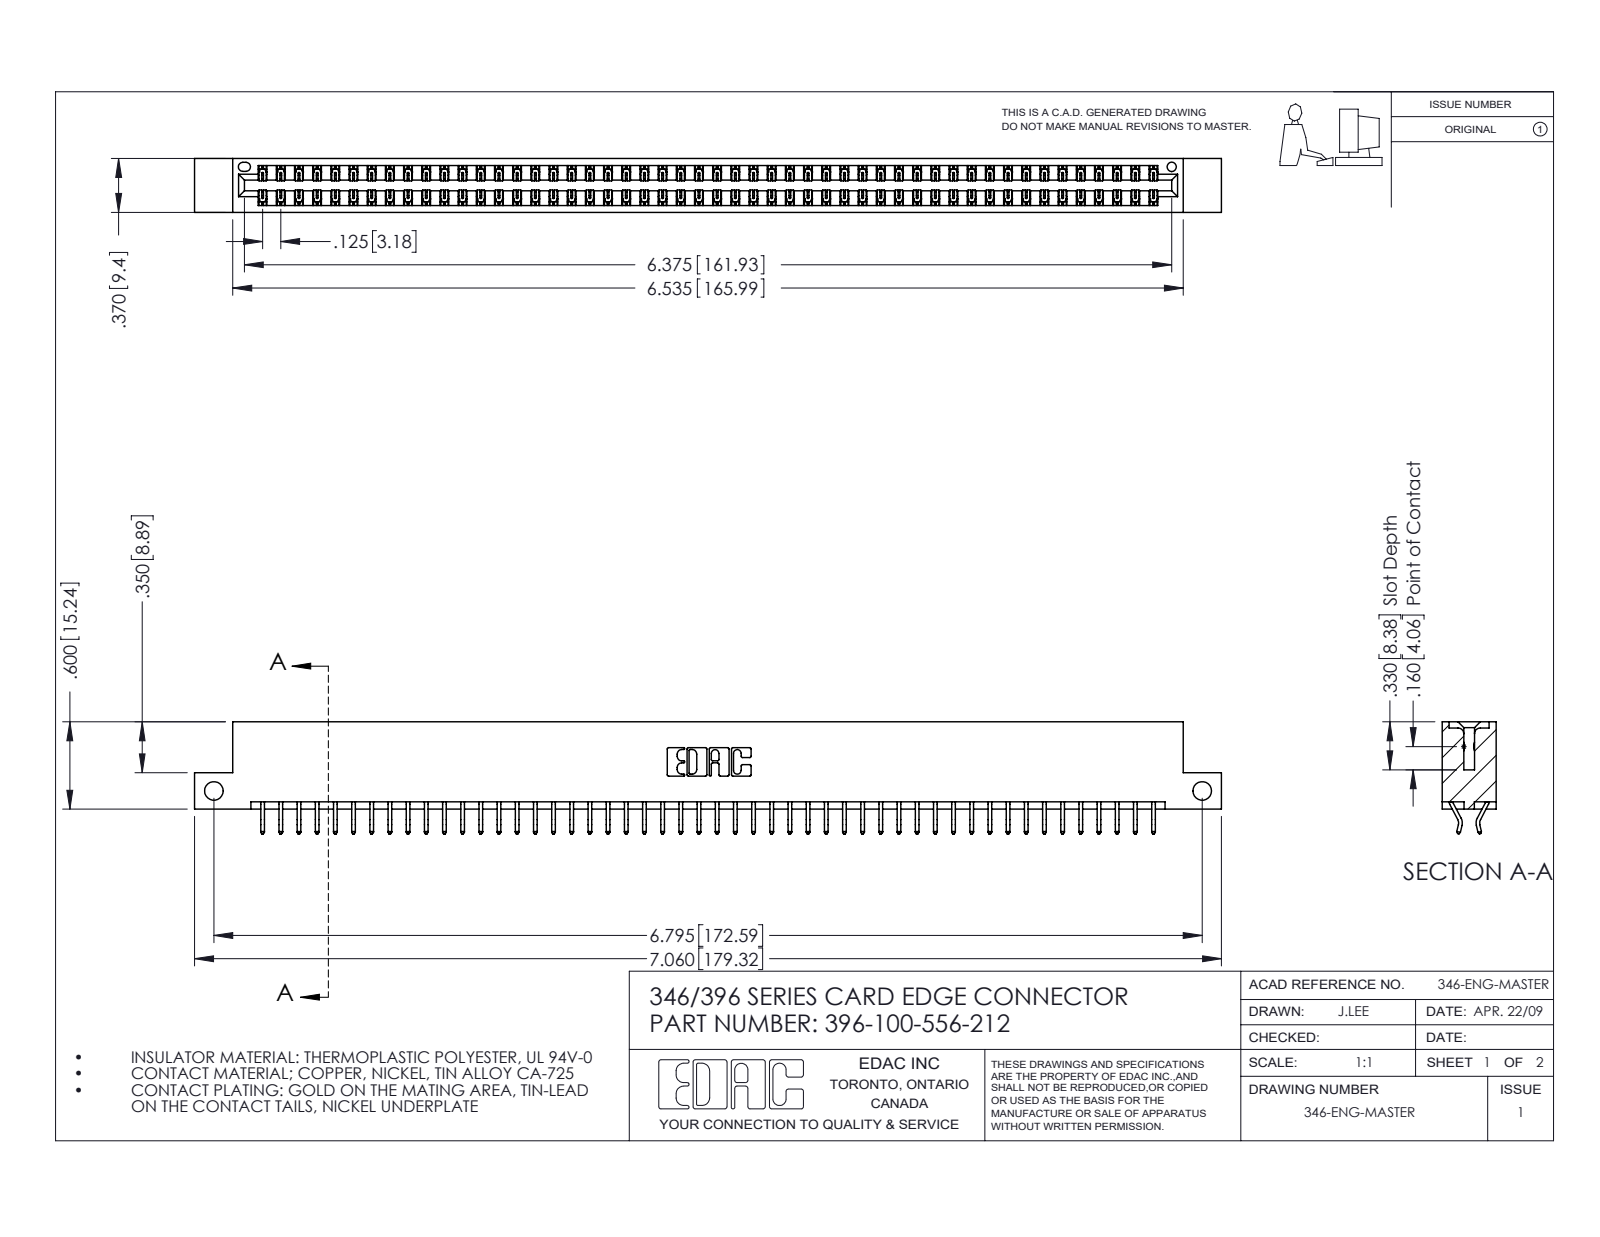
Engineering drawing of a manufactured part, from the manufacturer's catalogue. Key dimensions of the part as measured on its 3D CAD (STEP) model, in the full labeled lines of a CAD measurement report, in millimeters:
Part name (STEP PRODUCT): 345-292-001_556 Tail; 396-100-556-212; 346 Part_Flush Mounting Lugs - Side Mount
STEP written by: SolidWorks 2016 (CONFIG_CONTROL_DESIGN)
Units: millimetres
Bodies: 101 solids, 5922 faces (3976 planar, 1946 cylindrical, 0 other)
Overall size (bounding box): 179.3 × 19.6 × 9.4
Volume: 17 450 mm³ · Surface area: 23 890 mm²
Round holes (diameter × count): ⌀3.3 ×2, ⌀1.6 ×1
Partial cylindrical surfaces — rounded edges, fillets, slot ends (radius × count): R0.2 ×150, R0.3 ×22, R0.2 ×6, R0.8 ×6, R0.7 ×3, R0.3 ×2, R0.4 ×2, R0.6 ×2
Main face-to-face distances: 1.2, 8.2, 9.4, 6.4, 0.6, 1.8, 7.6, 7, 3.8, 5.6
Hole centre spacings: 172.6
